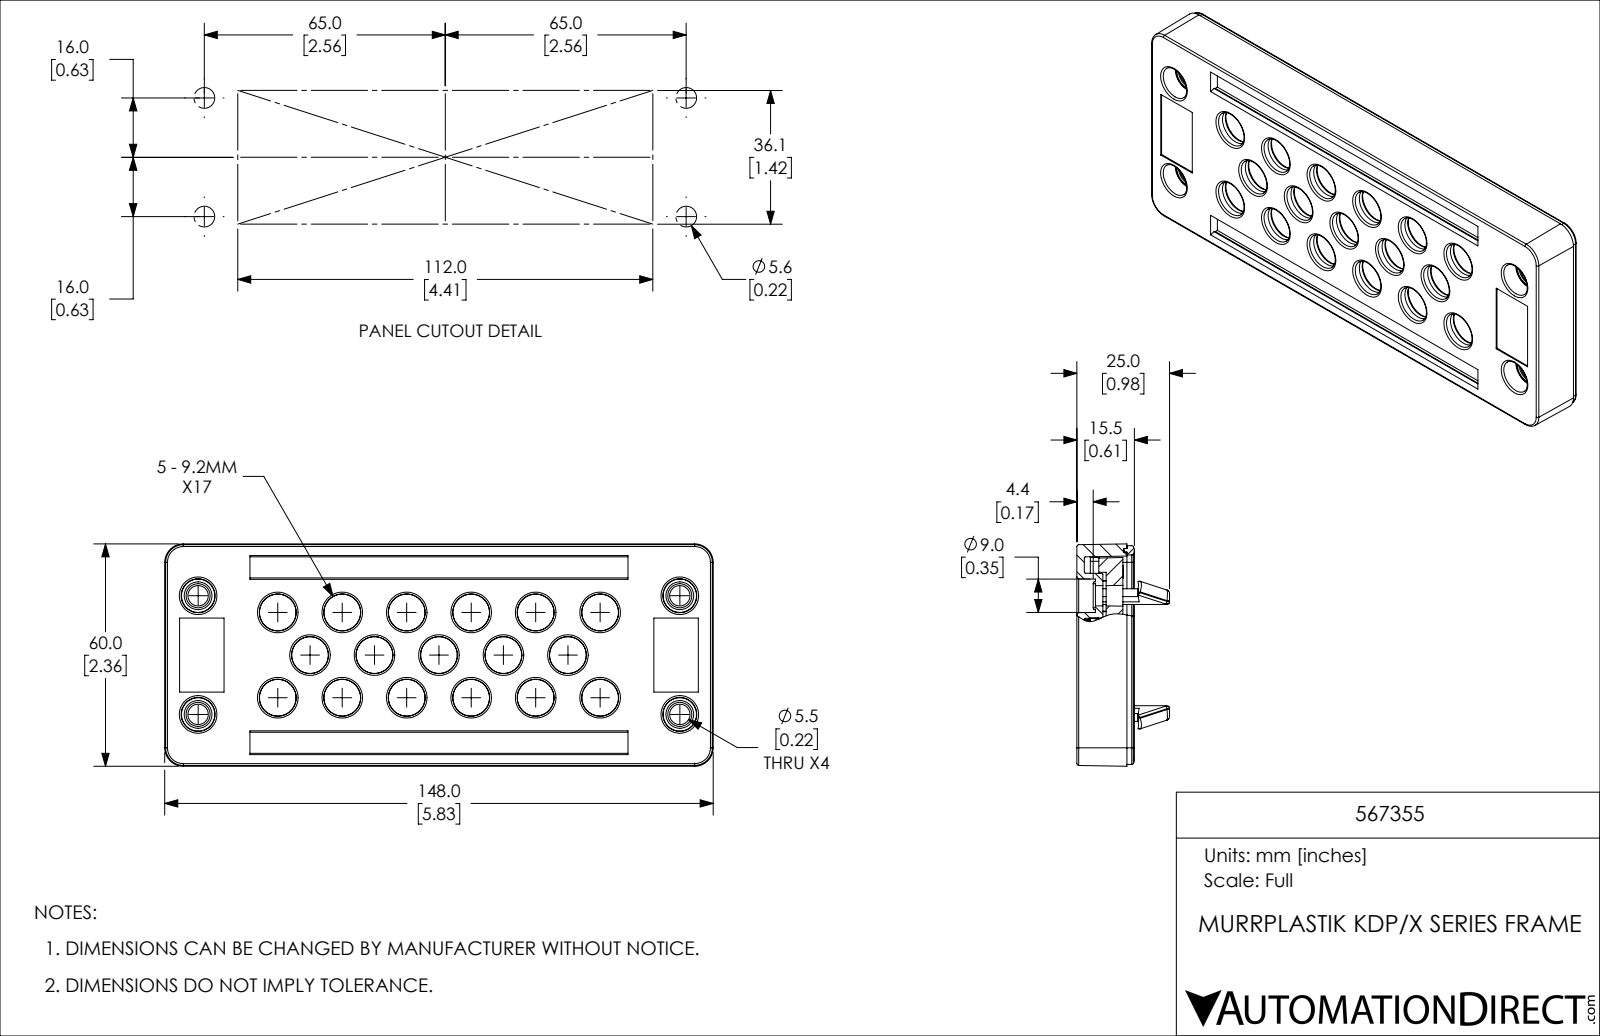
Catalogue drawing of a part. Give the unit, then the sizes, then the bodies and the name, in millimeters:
Units: millimetres
Overall size (bounding box): 148 × 60 × 25
Round holes (diameter × count): ⌀3.6 ×10, ⌀5.5 ×4, ⌀6.5 ×4, ⌀2.6 ×2, ⌀5 ×2, ⌀3.1 ×1
Round bosses / shafts (diameter × count): ⌀7.5 ×4, ⌀2.5 ×2, ⌀3 ×1
Partial cylindrical surfaces — rounded edges, fillets, slot ends (radius × count): R0.2 ×128, R0.3 ×48, R1 ×36, R0.45 ×32, R0.5 ×12, R2 ×12, R2.75 ×4, R3 ×4
Main face-to-face distances: 2.3, 5.9, 3.3, 3.6, 2, 6.5, 8.8, 12.4, 3.8, 3.9
Hole centre spacings: 10.09, 22.04, 23.13, 26.59, 35.31, 42.8, 44.44, 62.1
Volume: 73 244 mm³ · Surface area: 71 622 mm²
Bodies: 4 solids, 3865 faces (1075 planar, 1187 cylindrical, 1603 other)
Part name (STEP PRODUCT): 567355
STEP written by: SolidWorks 2019 (CONFIG_CONTROL_DESIGN)
